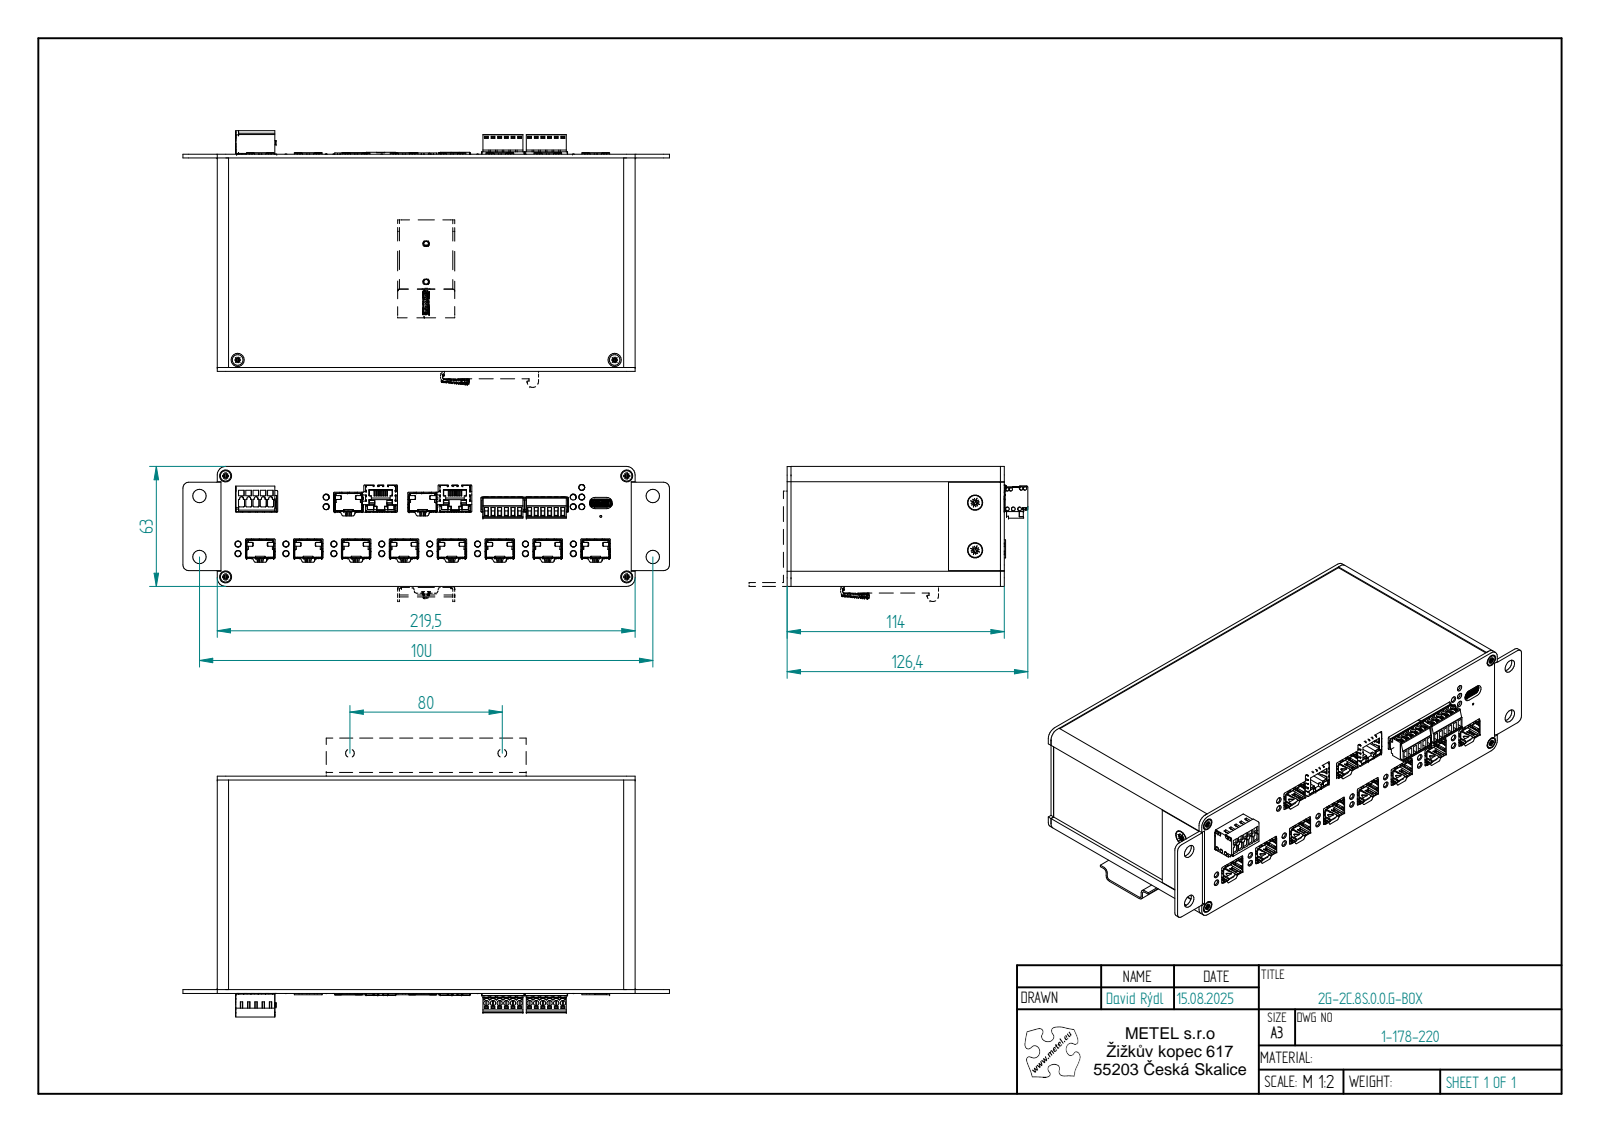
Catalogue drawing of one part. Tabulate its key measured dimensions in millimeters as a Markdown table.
| quantity | value |
| --- | --- |
| part name | 2G-2C.8S.0.0.G-BOX; Profil 210-2C.8S.0.0-zak; 1-878-220-20250521-005-2G-2C.8S.0.0.G-Predni; 734-205 (+8 more) |
| STEP written by | Solid Edge (AUTOMOTIVE_DESIGN) |
| units | millimeters |
| bodies | 166 solids, 17426 faces (11898 planar, 4996 cylindrical, 532 other) |
| overall size | 255.5 × 146.35 × 73.41 |
| volume | 300 489 mm³ |
| surface area | 318 002 mm² |
| round holes (diameter × count) | 2 × 120, 3.3 × 20, 1.5 × 17, 1.9 × 12, 2.1 × 12, 2.8 × 12, 3.5 × 8, 2.46 × 6, 3.2 × 5, 0.45 × 4, 2.7 × 4, 7 × 4 |
| round bosses / shafts (diameter × count) | 3 × 25, 1.8 × 14, 5.5 × 4, 2.9 × 4, 2 × 3, 7.5 × 2, 5.6 × 2, 4 × 2 |
| partial cylindrical surfaces (radius × count) | 0.5 × 266, 0.1 × 264, 0.19 × 216, 0.2 × 202, 0.25 × 198, 0.3 × 164, 1 × 67, 0.38 × 51 |
| main face-to-face distances | 2.88, 59.12, 2, 112, 62, 56.24, 4, 114, 110, 211.5 |
| hole center spacings | 5.05, 3.5, 25.16, 25.66, 75.47, 75.64, 7, 50.31 |
